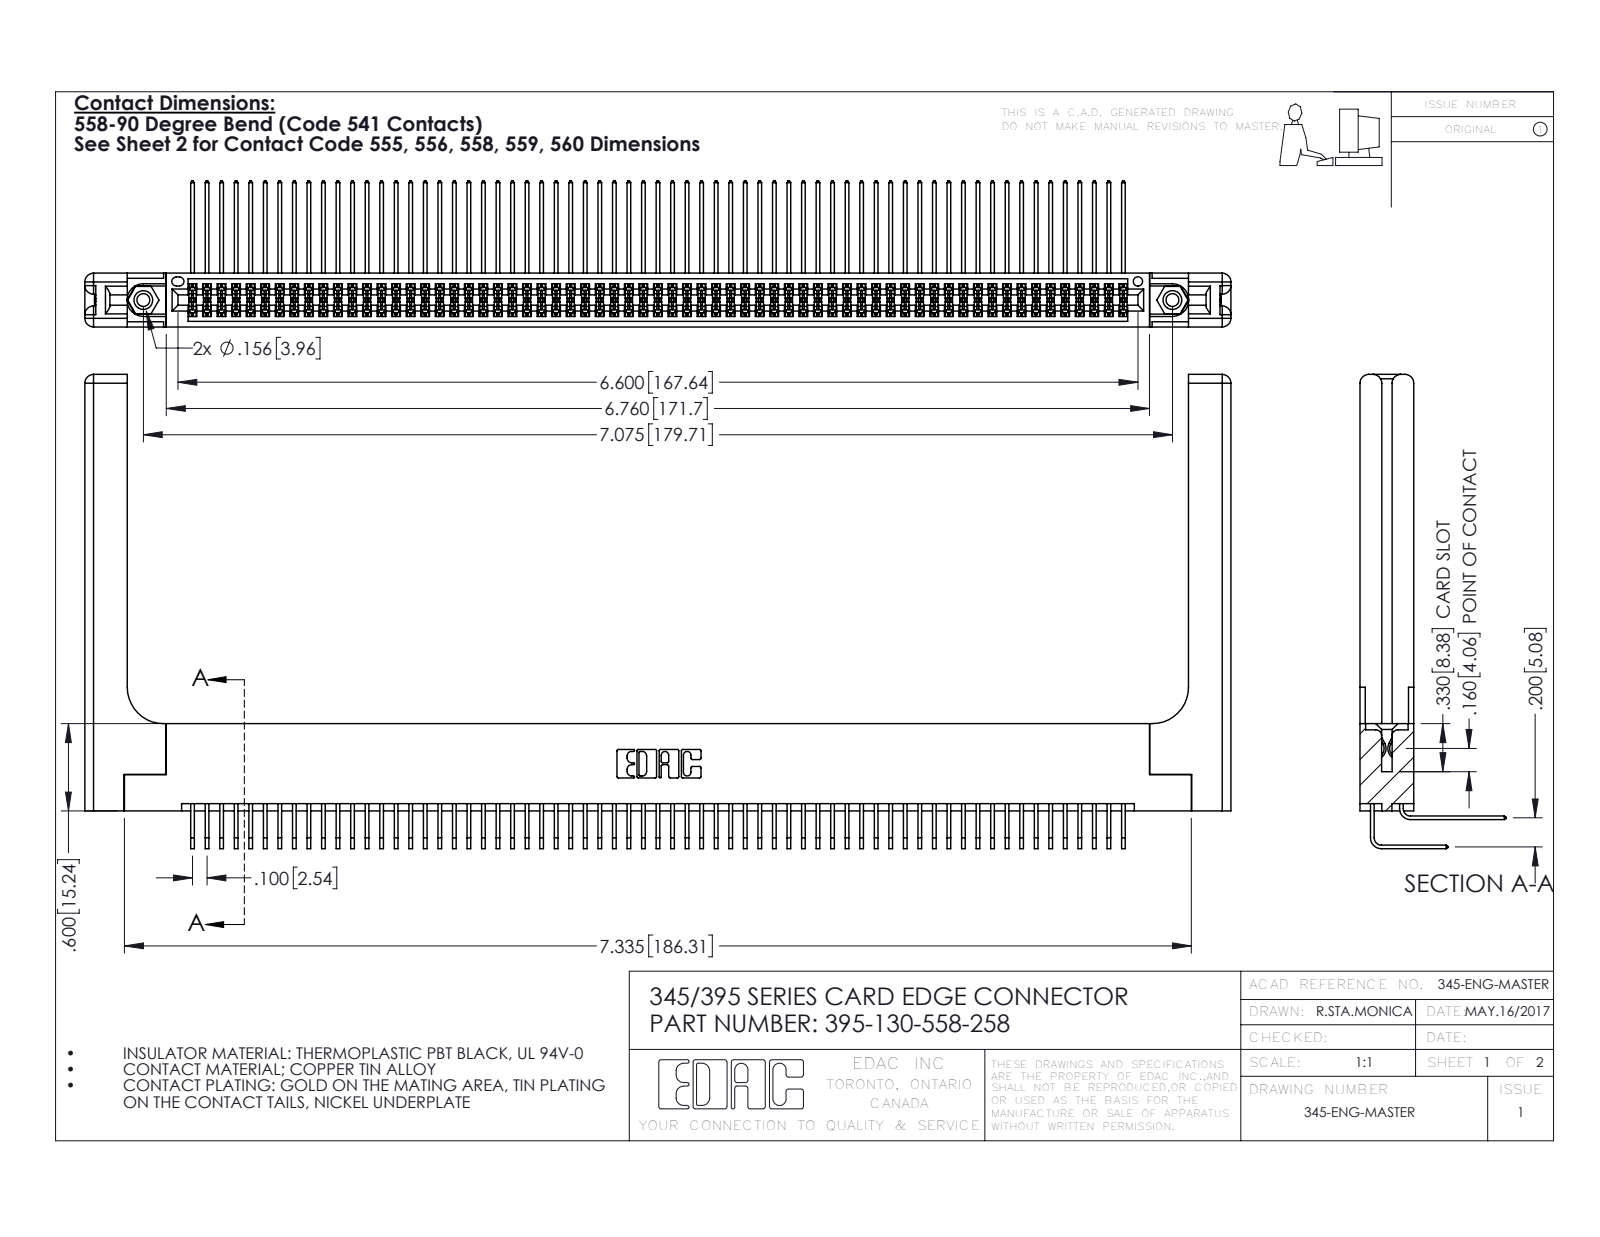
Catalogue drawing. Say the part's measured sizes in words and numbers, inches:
The part is named "395-130-558-258; 345 Part_Flush Mounting Lugs - 0.156 Dia-TH; 345-250-001_345-250-001-102; 345-292-001_558 559 Tail - 1 (+2 more)". Its 3-D file was written by "SolidWorks 2016 (CONFIG_CONTROL_DESIGN)". It is 135 solids with 7142 faces: 4778 planar, 2304 cylindrical and 60 other. Overall it measures 7.879 by 3.259 by 1.005 inches. Its volume is 1.762 cubic inches and its surface area 60.75 square inches. Round holes: 2 of diameter 0.089, 2 of diameter 0.125, 2 of diameter 0.156, 1 of diameter 0.064. Round bosses or shafts: 2 of diameter 0.155. Partial cylindrical surfaces (rounded edges, fillets, slot ends): 196 of radius 0.006, 22 of radius 0.01, 16 of radius 0.06, 6 of radius 0.007, 6 of radius 0.031, 3 of radius 0.026, 2 of radius 0.014, 2 of radius 0.019. The main face-to-face distances are 0.072, 0.298, 0.2, 0.37, 0.098, 0.272, 0.025, 0.225, 0.025, 0.148. The hole center spacings are 0.27, 6.839, 7.075.
